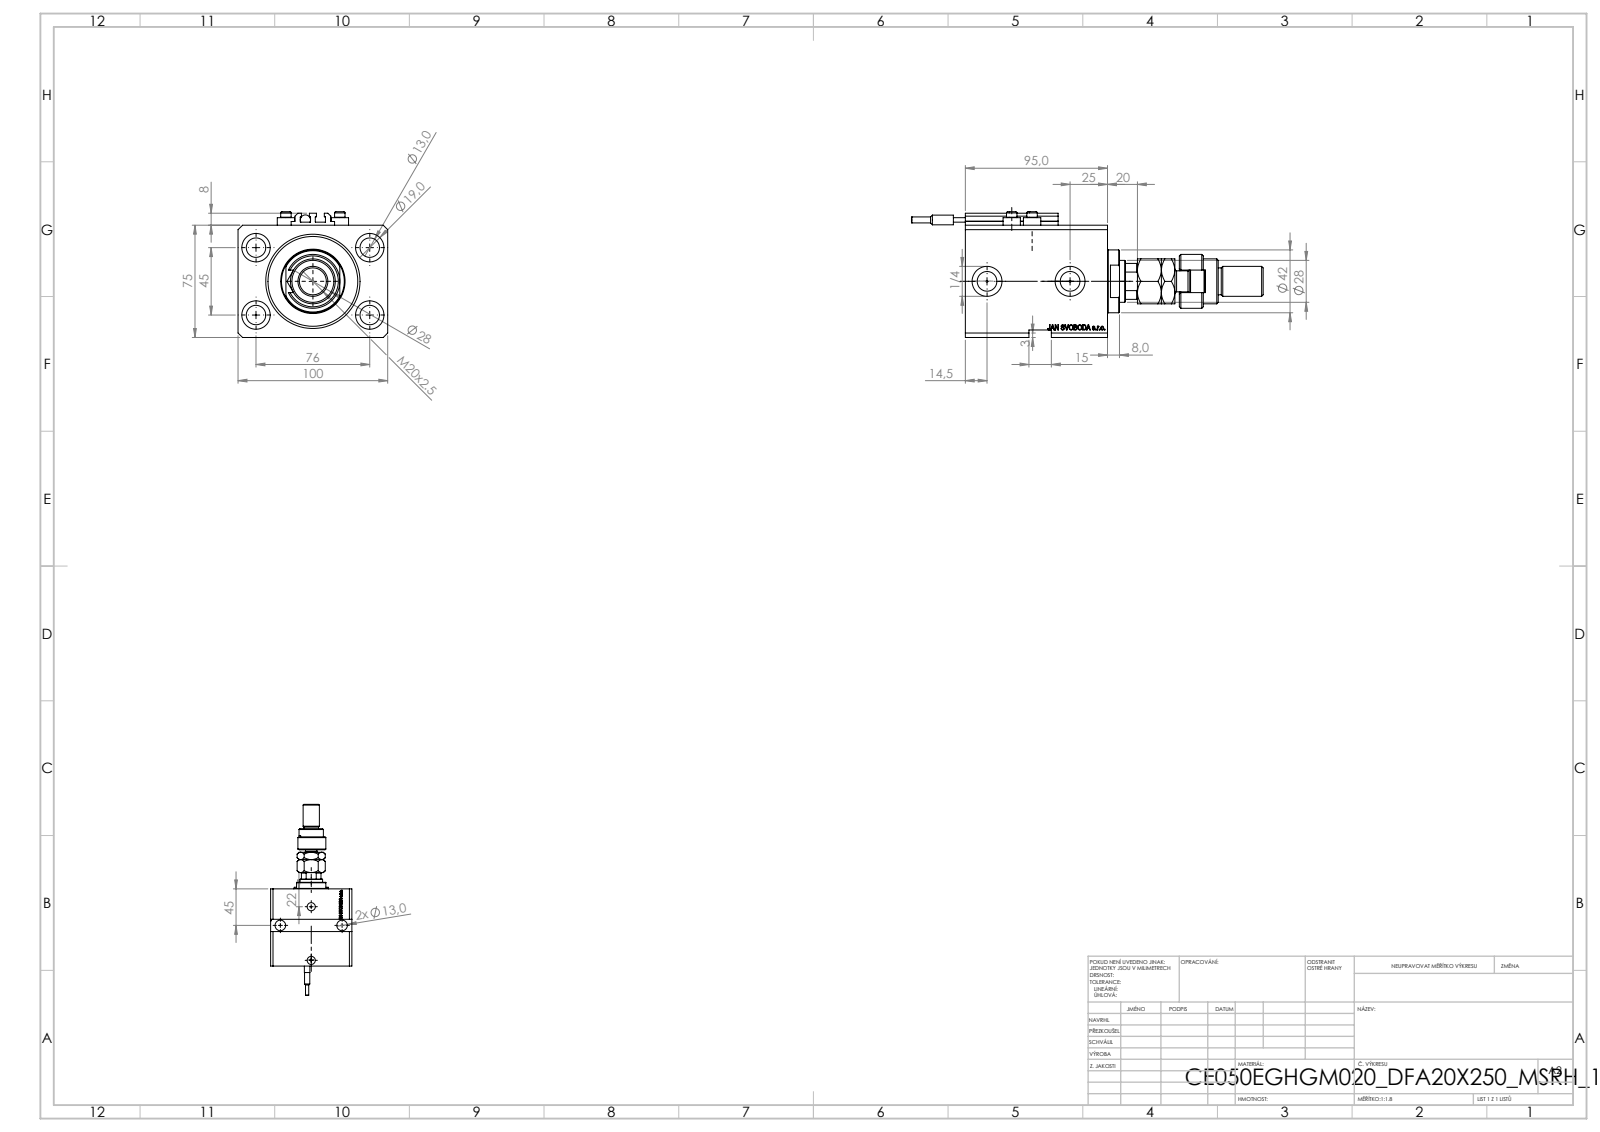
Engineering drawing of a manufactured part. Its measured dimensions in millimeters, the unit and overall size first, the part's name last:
Units: millimetres
Overall size (bounding box): 235 × 100 × 84
Round holes (diameter × count): ⌀13 ×6, ⌀1.25 ×4, ⌀4 ×4, ⌀19 ×4, ⌀10 ×2, ⌀13.16 ×2, ⌀20 ×2, ⌀18.5 ×1, ⌀28 ×1, ⌀50 ×1, ⌀63 ×1
Round bosses / shafts (diameter × count): ⌀11.6 ×4, ⌀7 ×4, ⌀42 ×1, ⌀36 ×1, ⌀30 ×1, ⌀22 ×1, ⌀20 ×1, ⌀18 ×1
Partial cylindrical surfaces — rounded edges, fillets, slot ends (radius × count): R0.2 ×10, R7.5 ×1, R12 ×1, R13.5 ×1
Main face-to-face distances: 75, 20, 100, 95, 11.9, 83.1, 63.1, 40, 30, 57.5
Hole centre spacings: 44.16, 76, 13.6, 20.72, 27.59, 29.58, 30, 33.62
Volume: 661 683 mm³ · Surface area: 136 511 mm²
Bodies: 11 solids, 1199 faces (579 planar, 145 cylindrical, 475 other)
Part name (STEP PRODUCT): SWITCH_V250CE; V250CE_VC_E; FEMALE_PART_FOR_DFA; V250CE_C_VCP (+3 more)
STEP written by: SolidWorks 2019 (CONFIG_CONTROL_DESIGN)
